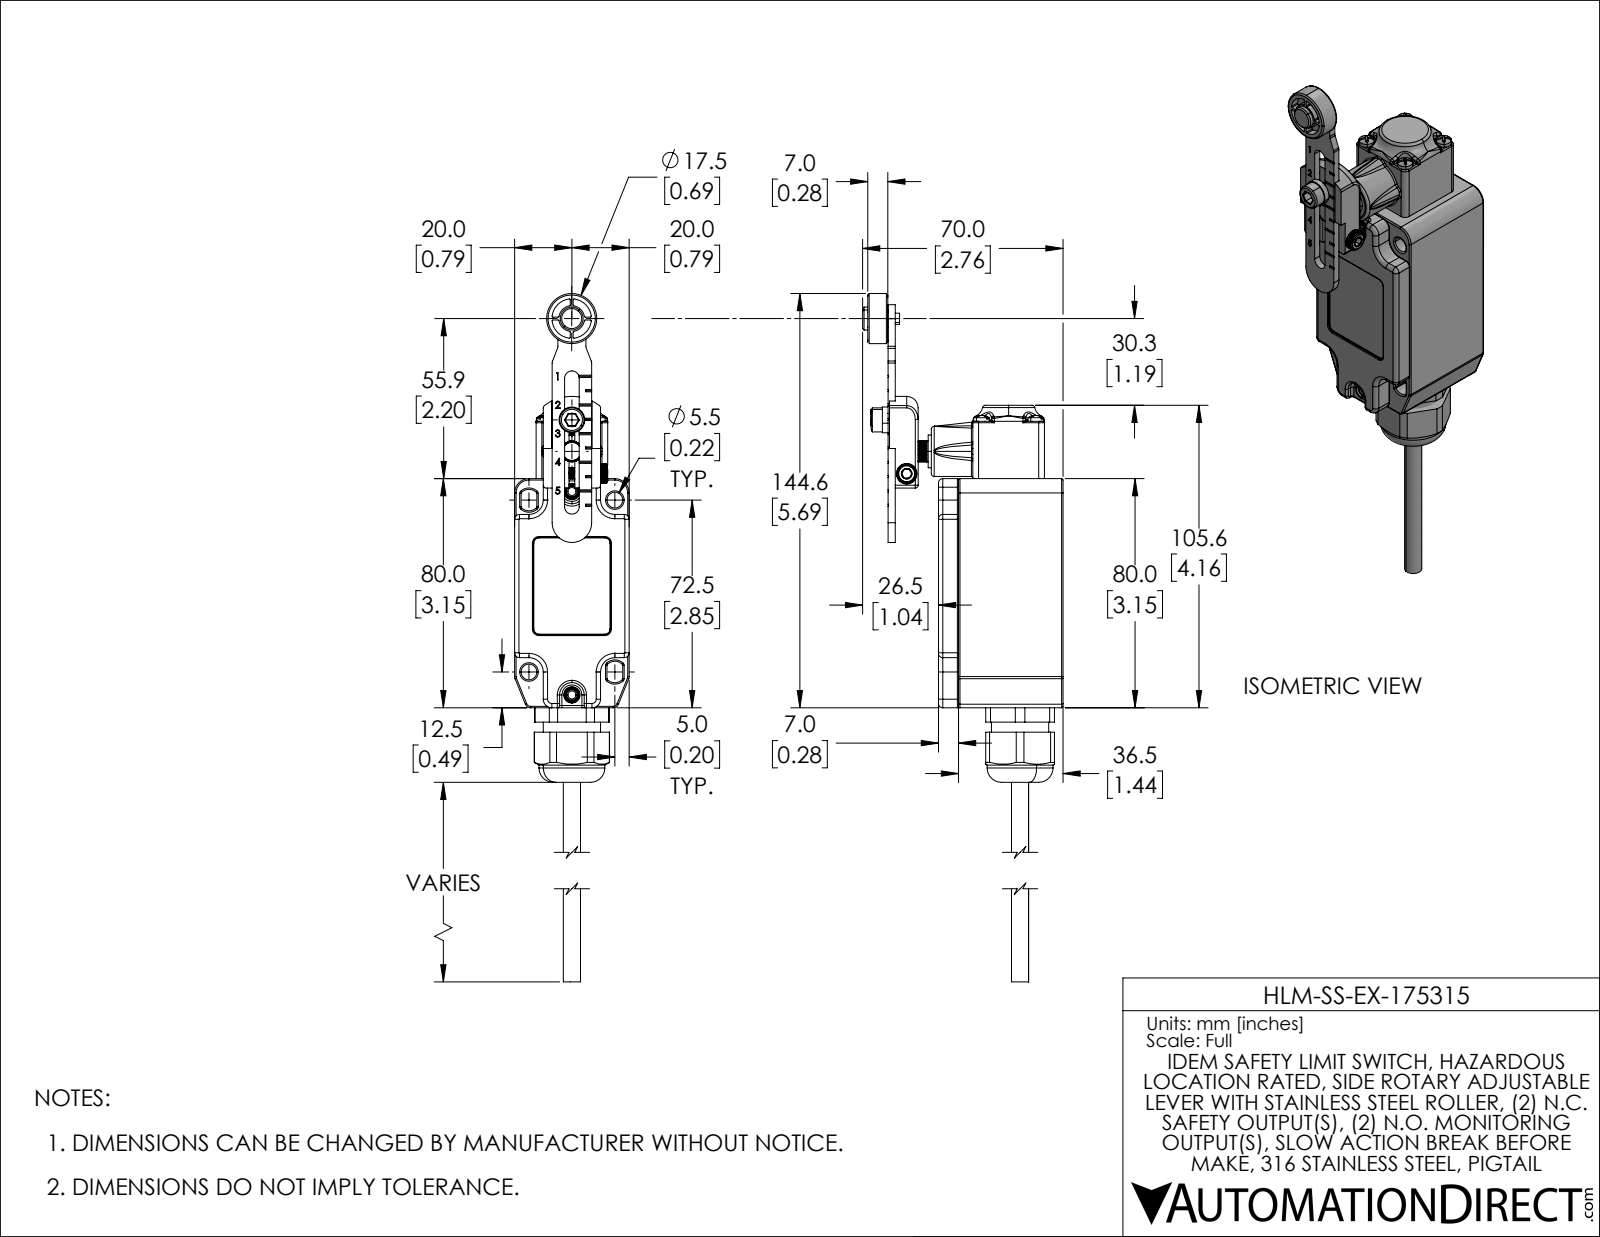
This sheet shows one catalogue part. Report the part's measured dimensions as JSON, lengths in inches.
{"part_name": "HLM-SS-EX-175315", "step_written_by": "SolidWorks 2021 (AUTOMOTIVE_DESIGN)", "units": "inches", "bodies": {"solids": 23, "faces": 3408, "planar": 1019, "cylindrical": 850, "other": 1539}, "overall_size": [9.001, 2.756, 1.638], "volume_in3": 5.448, "surface_area_in2": 96.9, "round_holes": [[0.102, 10], [0.134, 6], [0.106, 4], [0.161, 3], [0.114, 2], [0.157, 2], [0.169, 2], [0.217, 2], [0.571, 2], [0.126, 1], [0.173, 1], [0.201, 1]], "round_bosses_or_shafts": [[0.236, 7], [0.216, 4], [0.118, 4], [0.689, 2], [0.354, 2], [0.276, 2], [0.154, 2], [0.051, 2]], "partial_cylinders_radius": [[0.02, 115], [0.012, 32], [0.039, 28], [0.016, 24], [0.079, 20], [0.006, 14], [0.031, 10], [0.138, 8]], "face_to_face_distances": [0.12, 1.518, 1.398, 0.098, 1.638, 1.732, 2.307, 0.236, 1.634, 1.496], "hole_center_spacings": [0.748, 0.529, 1.258, 0.354, 0.432, 0.65, 0.75, 0.828]}
